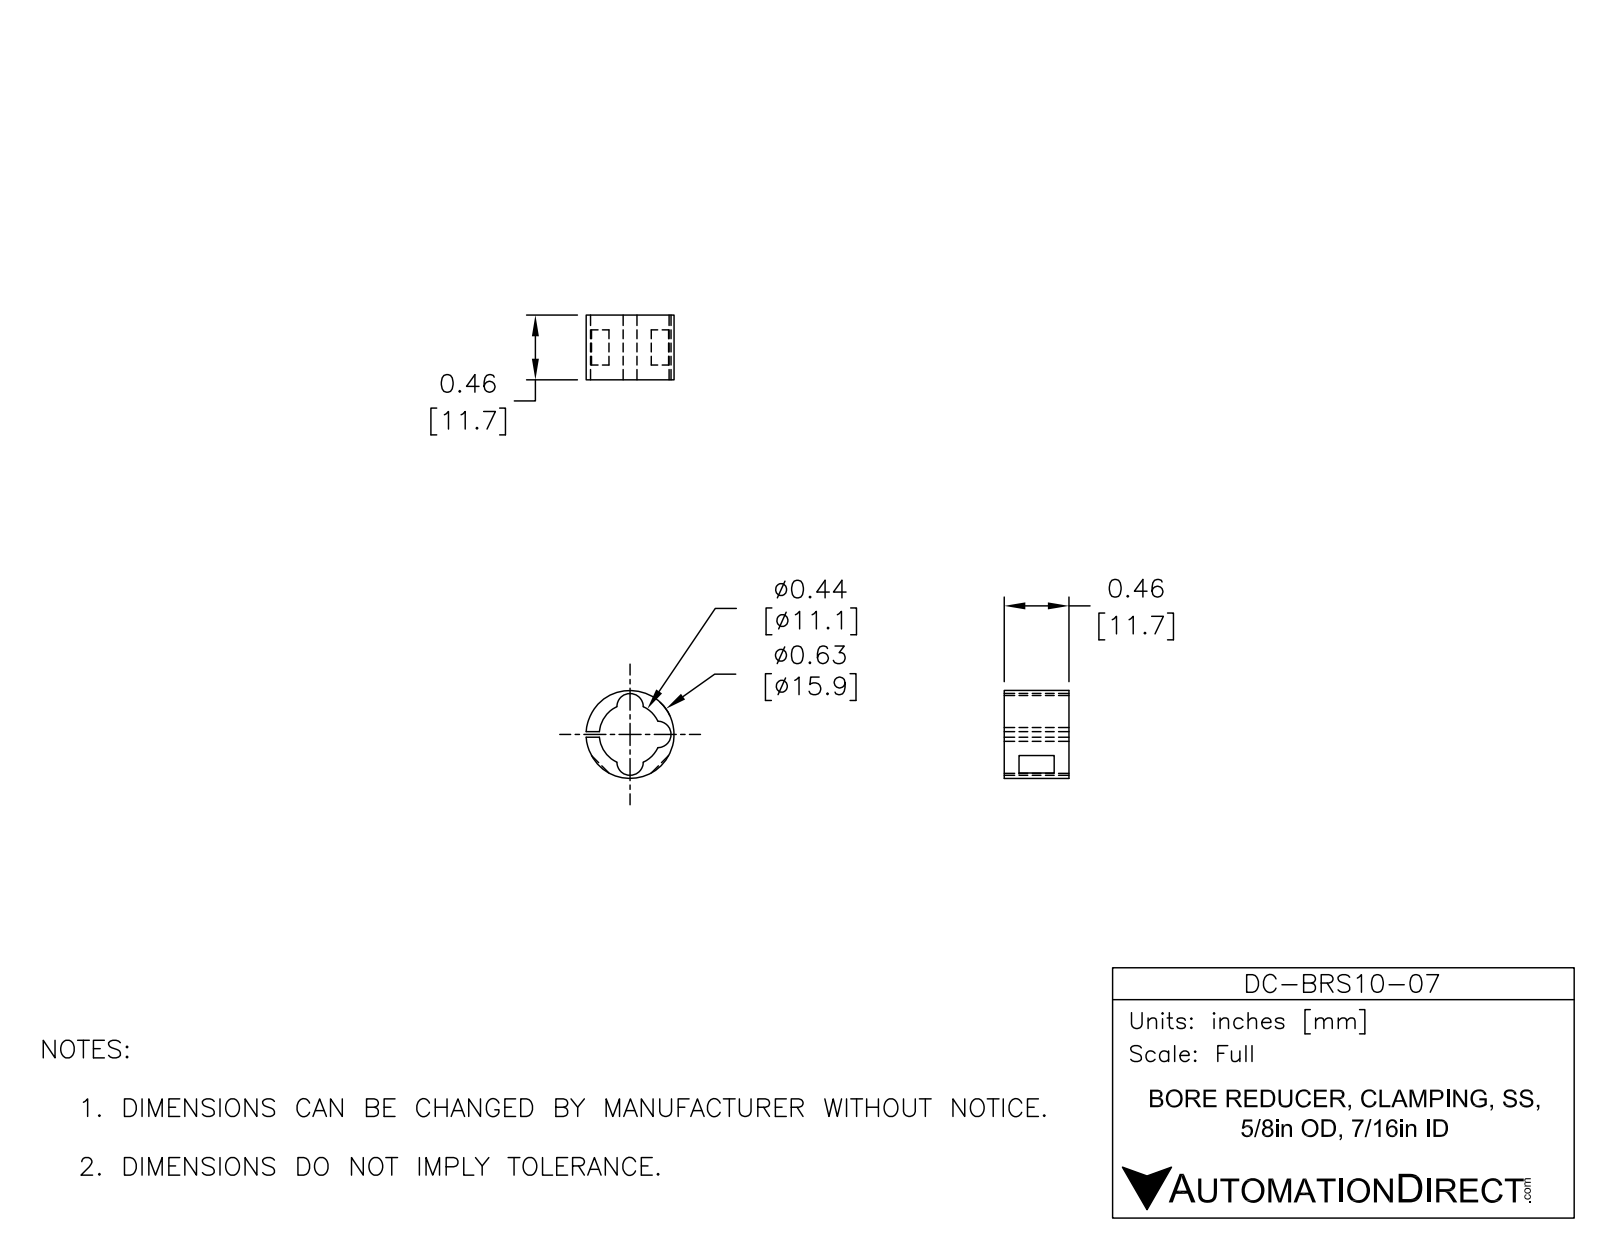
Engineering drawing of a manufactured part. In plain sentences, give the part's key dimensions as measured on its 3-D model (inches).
The part is named "DC-BRS10-07". Its 3-D file was written by "SolidWorks 2015 (AUTOMOTIVE_DESIGN)". It is 1 solid with 21 faces: 10 planar, 11 cylindrical and 0 other. Overall it measures 0.625 by 0.624 by 0.46 inches. Its volume is 0.054 cubic inches and its surface area 1.967 square inches. Round bosses or shafts: 1 of diameter 0.625. Partial cylindrical surfaces (rounded edges, fillets, slot ends): 3 of radius 0.094, 1 of radius 0.219. The main face-to-face distances are 0.46, 0.04, 0.105, 0.355, 0.25.
